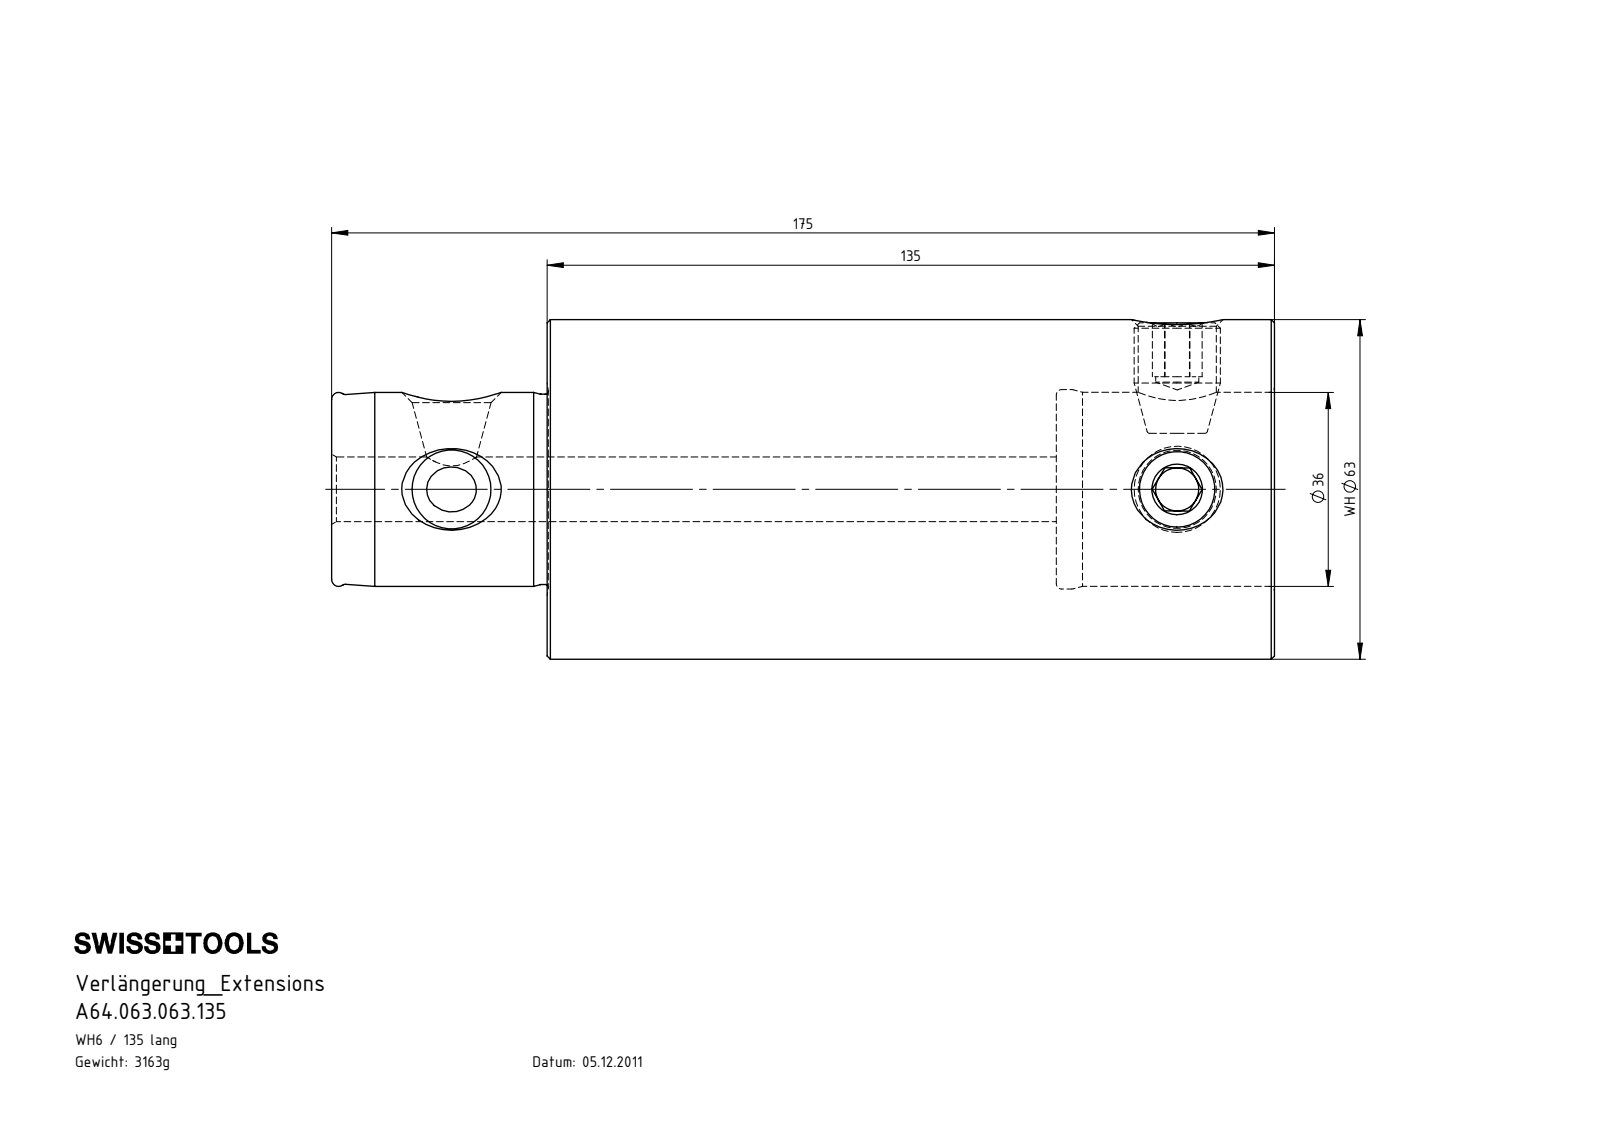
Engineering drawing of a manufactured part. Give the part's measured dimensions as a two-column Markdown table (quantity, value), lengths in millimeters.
| quantity | value |
| --- | --- |
| part name | WH6-ER1.001.021; WH6-WH6.001.135; WH6-WH6.001.135_A |
| STEP written by | SolidWorks 2015 (AUTOMOTIVE_DESIGN) |
| units | millimeters |
| bodies | 3 solids, 130 faces (32 planar, 24 cylindrical, 74 other) |
| overall size | 175 × 63 × 63 |
| volume | 402 736 mm³ |
| surface area | 50 753 mm² |
| round holes (diameter × count) | 8 × 2, 14.5 × 2, 12 × 1, 36 × 1, 37 × 1 |
| round bosses / shafts (diameter × count) | 16 × 2, 63 × 1, 35.3 × 1 |
| main face-to-face distances | 135, 94.5, 40.5, 40, 134.5, 175, 8, 20.5, 10.5, 10 |
